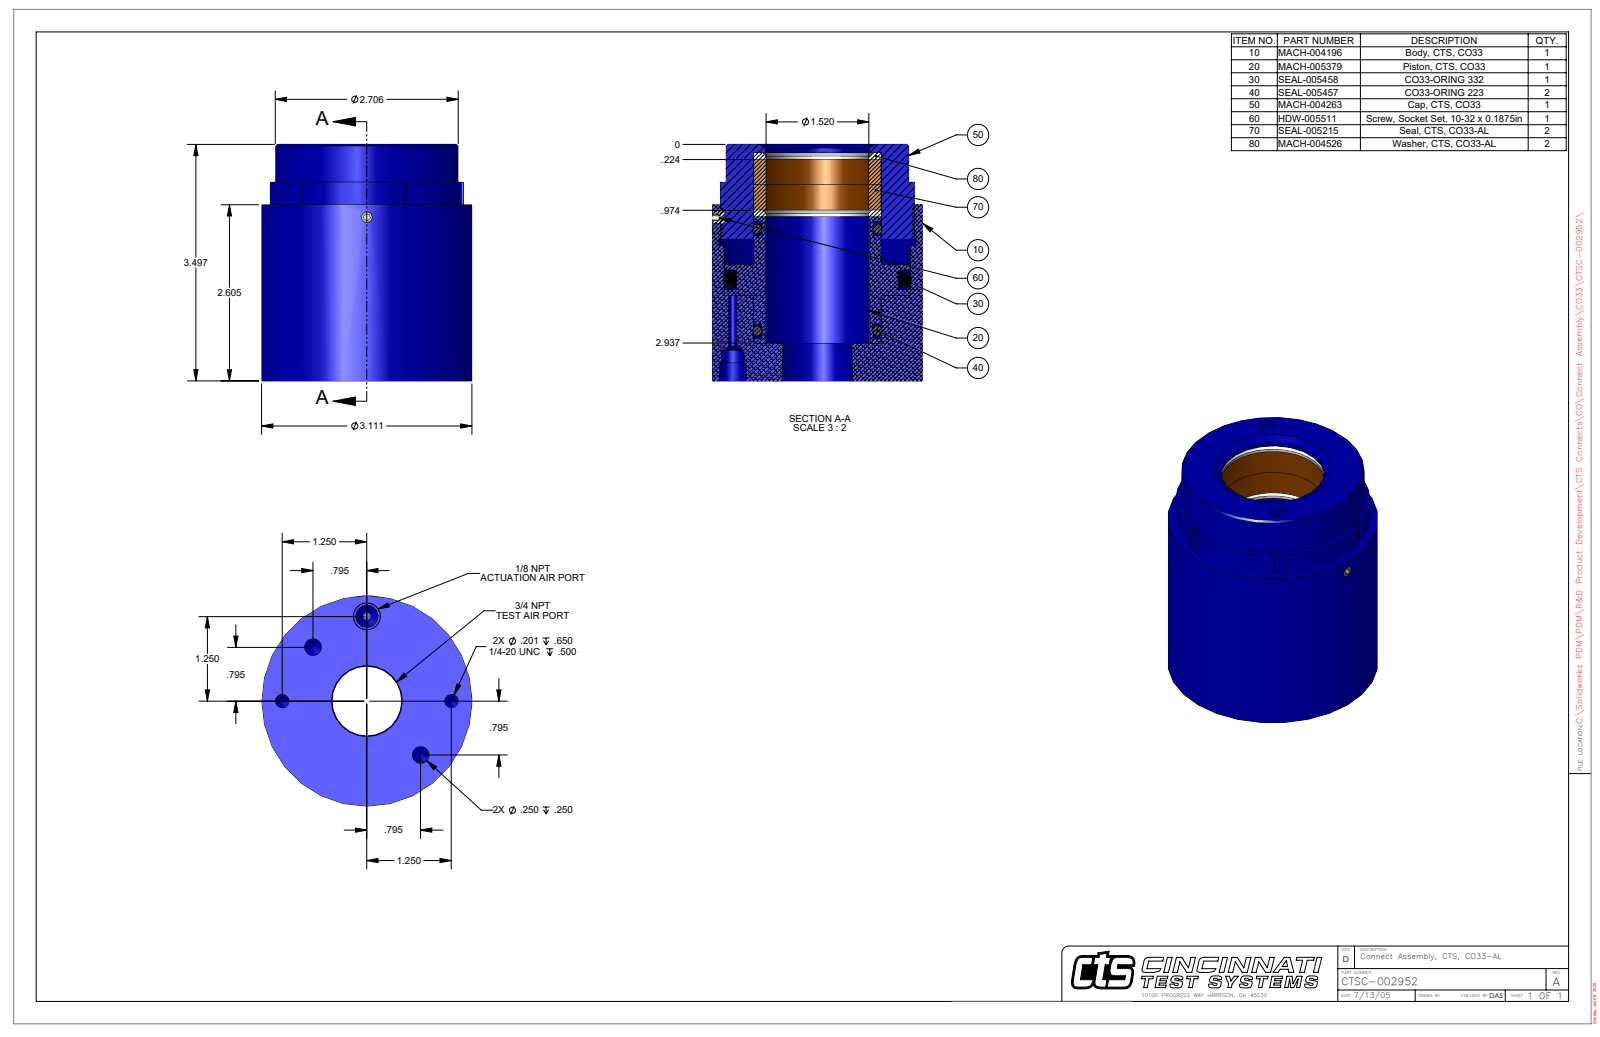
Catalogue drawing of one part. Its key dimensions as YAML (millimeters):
part_name: "CTSC-002952"
step_written_by: "SolidWorks 2023 (AUTOMOTIVE_DESIGN)"
units: millimeters
bodies: {solids: 1, faces: 122, planar: 49, cylindrical: 53, other: 20}
overall_size: [88.8, 79, 79]
volume: 313600
surface_area: 42630
round_holes:
  - {diameter: 6.4, count: 4}
  - {diameter: 5.1, count: 2}
  - {diameter: 2.4, count: 1}
  - {diameter: 3.2, count: 1}
  - {diameter: 4, count: 1}
  - {diameter: 8.4, count: 1}
  - {diameter: 38.6, count: 1}
  - {diameter: 38.7, count: 1}
  - {diameter: 38.8, count: 1}
  - {diameter: 38.8, count: 1}
  - {diameter: 48.1, count: 1}
round_bosses_or_shafts:
  - {diameter: 79, count: 1}
  - {diameter: 73, count: 1}
  - {diameter: 68.7, count: 1}
  - {diameter: 47.9, count: 1}
partial_cylinders:
  - {radius: 35.7, count: 1}
  - {radius: 39.2, count: 1}
face_to_face_distances: [88.8, 14.2, 74.6, 66.2, 22.7, 51.9, 60.4, 8.4, 21.4, 85.5]
hole_center_spacings: [28.6, 23.3, 31.8, 55.8, 2.4, 25.6, 44.9, 54.7]
